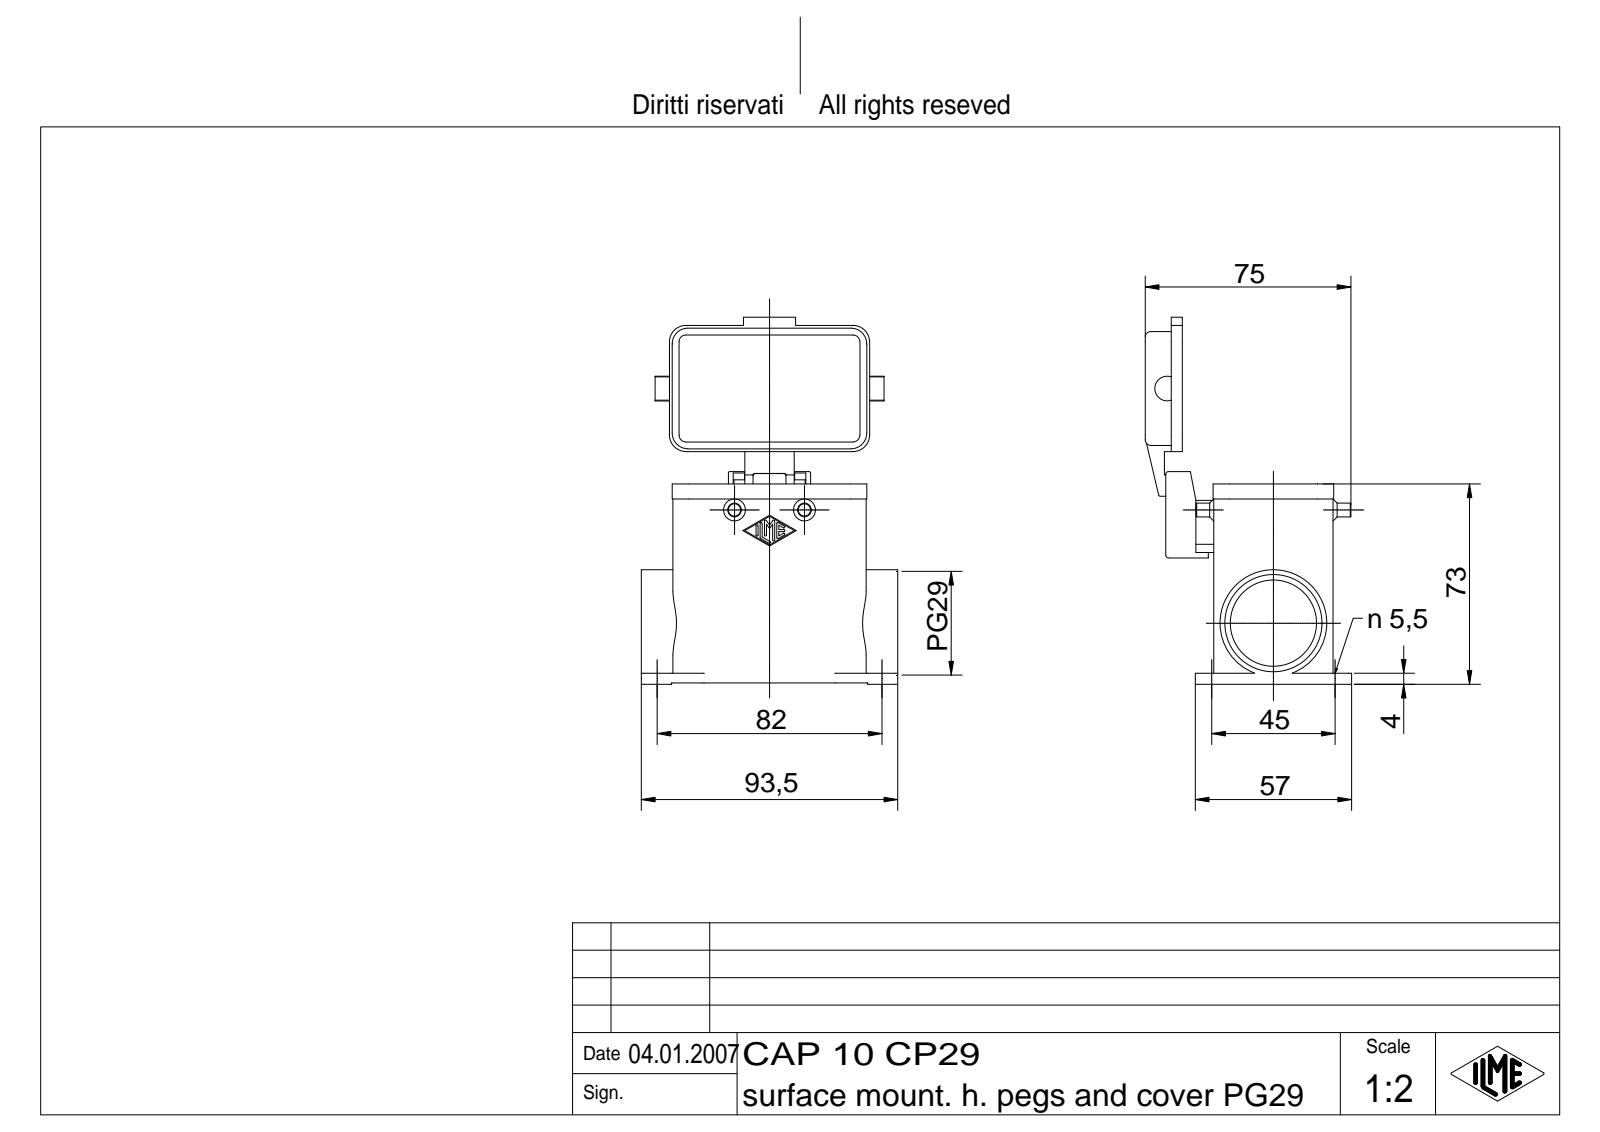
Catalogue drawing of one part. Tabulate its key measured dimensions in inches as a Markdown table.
| quantity | value |
| --- | --- |
| part name | CAP 10 CP29 |
| STEP written by | Autodesk Inventor 7 (AUTOMOTIVE_DESIGN) |
| units | inches |
| bodies | 1 solid, 474 faces (197 planar, 166 cylindrical, 111 other) |
| overall size | 5.266 × 3.681 × 2.963 |
| volume | 6.106 in³ |
| surface area | 96.38 in² |
| round holes (diameter × count) | 0.217 × 4, 0.157 × 1, 0.197 × 1, 1.239 × 1, 1.397 × 1 |
| round bosses / shafts (diameter × count) | 0.197 × 2, 0.118 × 2, 1.535 × 1, 0.276 × 1, 0.157 × 1 |
| partial cylindrical surfaces (radius × count) | 0.015 × 14, 0.039 × 14, 0.236 × 12, 0.02 × 10, 0.028 × 8, 0.079 × 8, 0.098 × 4, 0.118 × 4 |
| main face-to-face distances | 0.118, 1.594, 1.713, 0.098, 2.697, 1.476, 2.598, 0.886, 0.138, 2.48 |
| hole center spacings | 1.772, 3.228, 3.683 |
